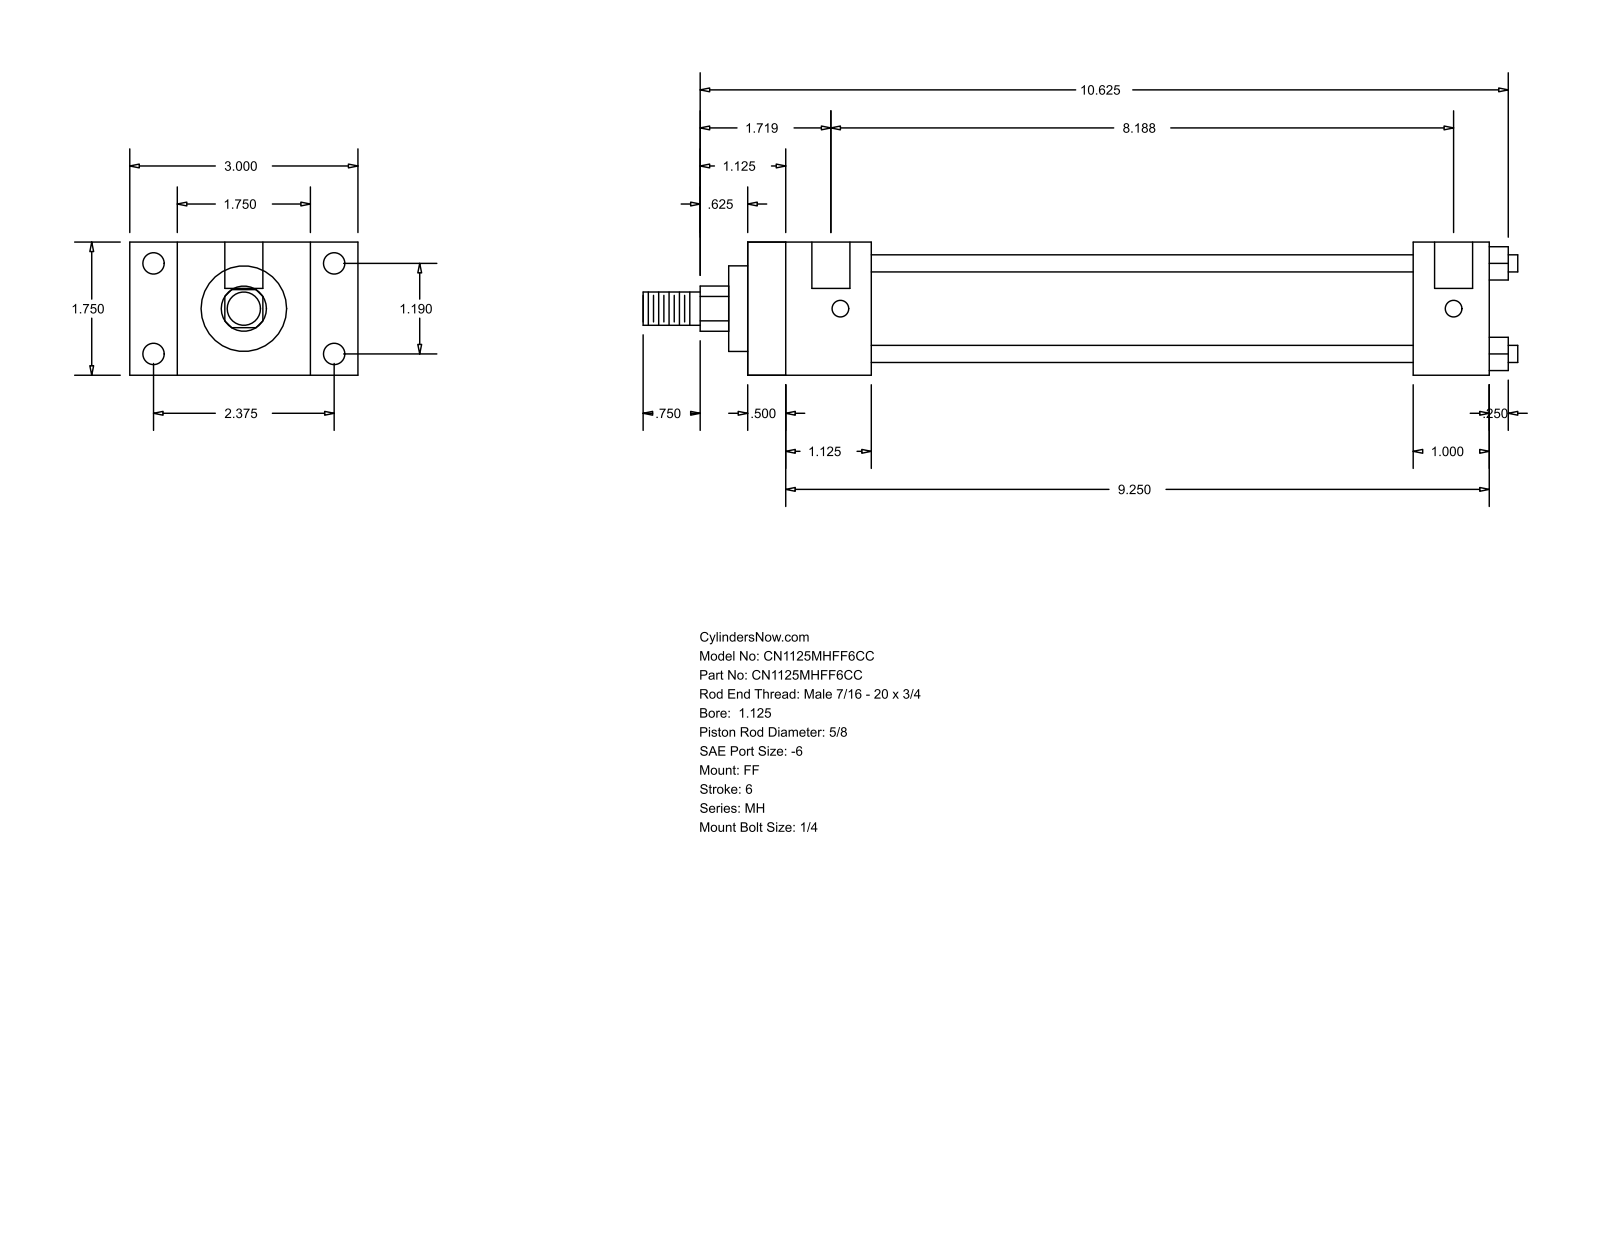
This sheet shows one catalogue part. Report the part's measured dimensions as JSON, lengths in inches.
{"part_name": "MH_FF__0112_0.625", "step_written_by": "GSSL Pune (CONFIG_CONTROL_DESIGN)", "units": "inches", "bodies": {"solids": 0, "faces": 92, "planar": 64, "cylindrical": 28, "other": 0}, "overall_size": [11.5, 3, 1.75], "round_holes": [[0.219, 4], [0.281, 4], [0.5, 2]], "round_bosses_or_shafts": [[0.225, 4], [1.375, 1], [1.125, 1], [0.625, 1], [0.437, 1]], "partial_cylinders_radius": [[0.297, 1]], "face_to_face_distances": [1.75, 9.75, 0.5, 9.25, 0.625, 1.125, 2.375, 1, 1.625, 8.75], "hole_center_spacings": [1.19, 2.375, 2.656, 8.063, 0.125, 8.187]}
